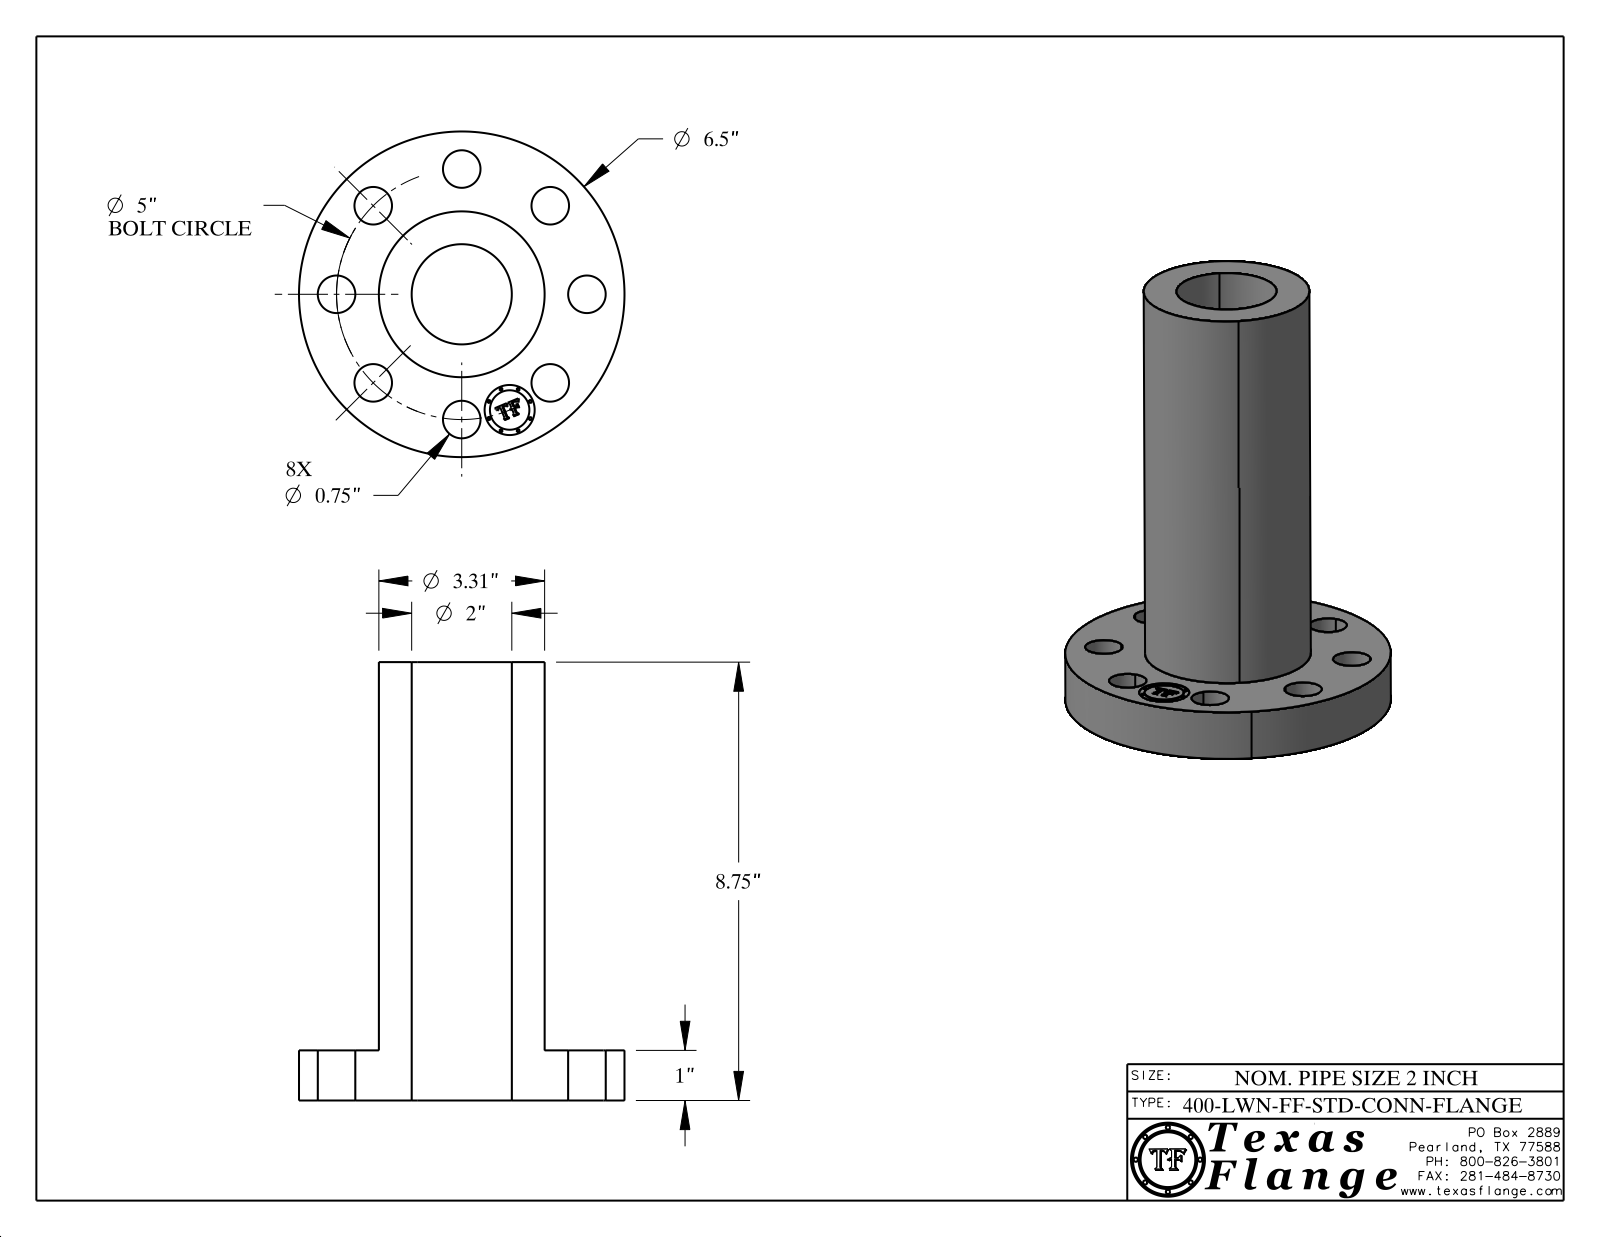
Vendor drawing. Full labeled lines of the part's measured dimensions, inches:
Part name (STEP PRODUCT): 2-400-LWN-FF-STD-CONN-FLANGE
STEP written by: CATIA V5 STEP AP214 (AUTOMOTIVE_DESIGN)
Units: inches
Bodies: 1 solid, 410 faces (368 planar, 42 cylindrical, 0 other)
Overall size (bounding box): 8.75 × 6.5 × 6.5
Volume: 68.85 in³ · Surface area: 227.9 in²
Round holes (diameter × count): ⌀0.75 ×8, ⌀1 ×1, ⌀2 ×1
Round bosses / shafts (diameter × count): ⌀0.061 ×8, ⌀6.5 ×1, ⌀3.31 ×1, ⌀0.788 ×1
Main face-to-face distances: 1, 8.75, 7.75, 0.995, 7.755, 0.298, 0.293, 0.055, 0.193, 0.248
Hole centre spacings: 2.5, 1.913, 3.535, 4.619, 5, 0.976, 2.778, 4.157
